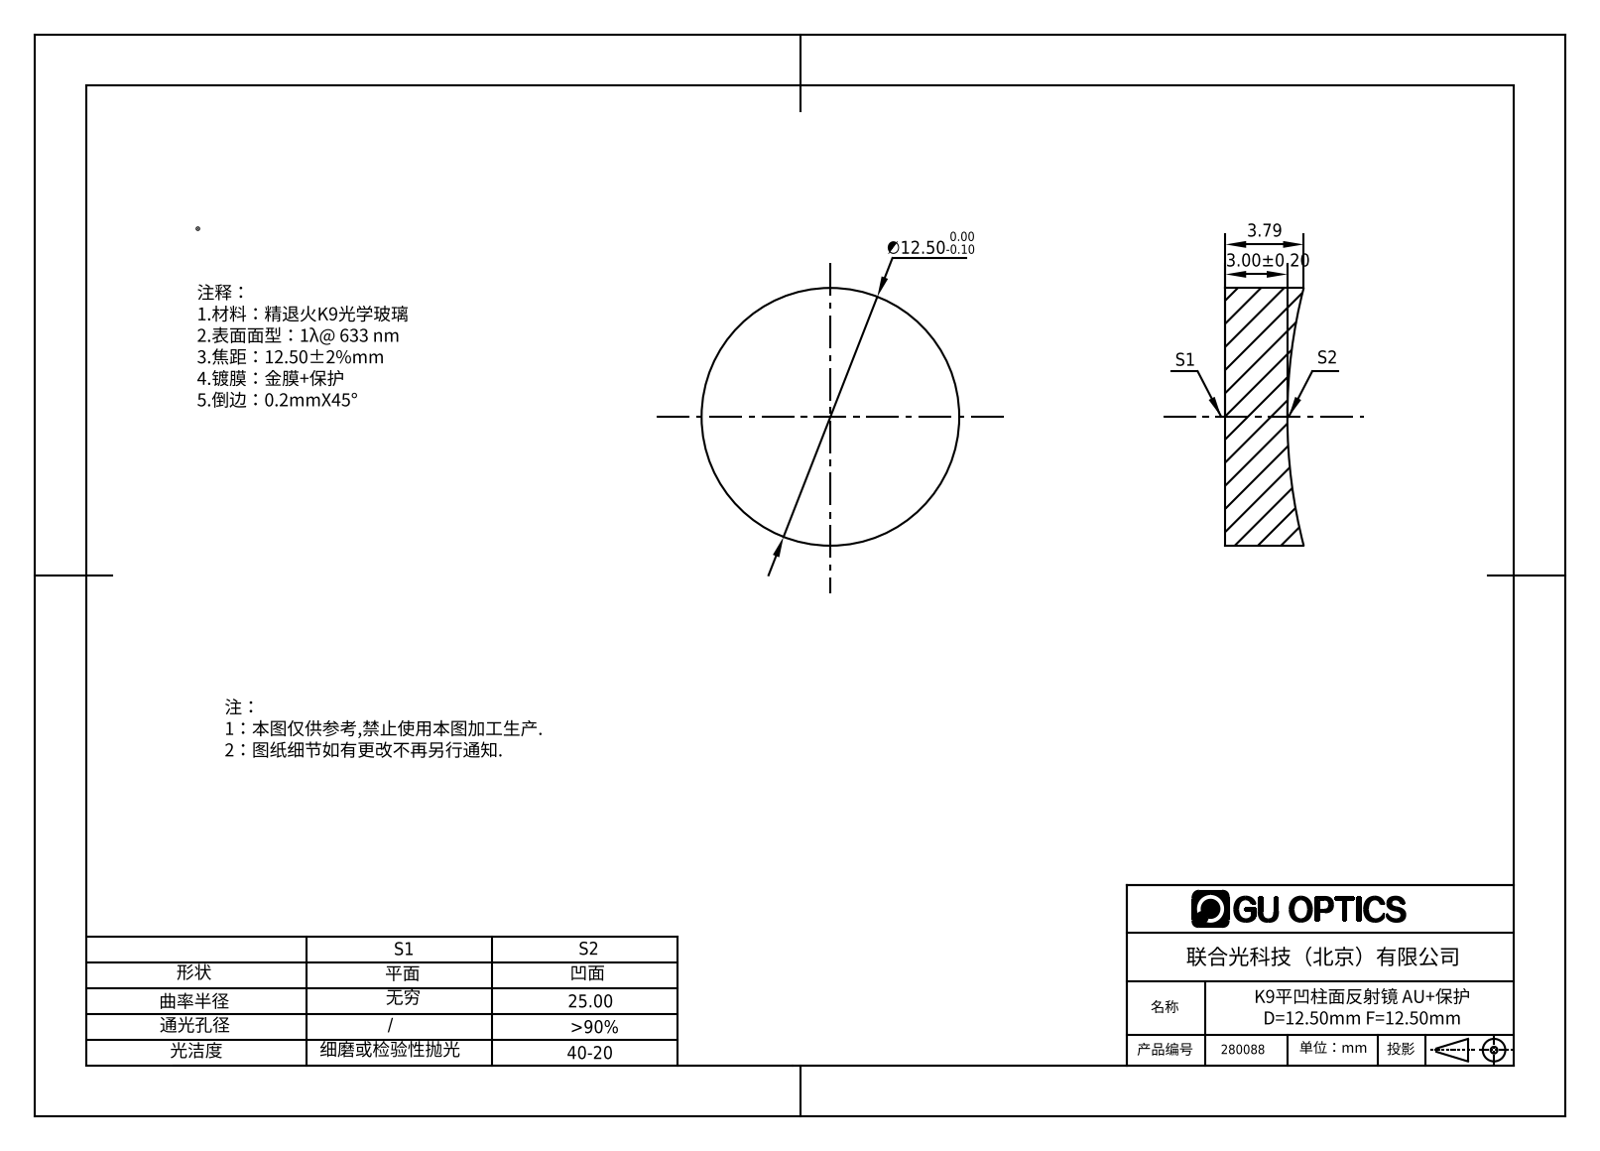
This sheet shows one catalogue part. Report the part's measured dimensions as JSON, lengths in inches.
{"part_name": "280000", "step_written_by": "SolidWorks 2020 (CONFIG_CONTROL_DESIGN)", "units": "inches", "bodies": {"solids": 1, "faces": 3, "planar": 1, "cylindrical": 2, "other": 0}, "overall_size": [0.492, 0.492, 0.149], "volume_in3": 0.024, "surface_area_in2": 0.589, "round_bosses_or_shafts": [[0.492, 1]], "partial_cylinders_radius": [[0.984, 1]]}
